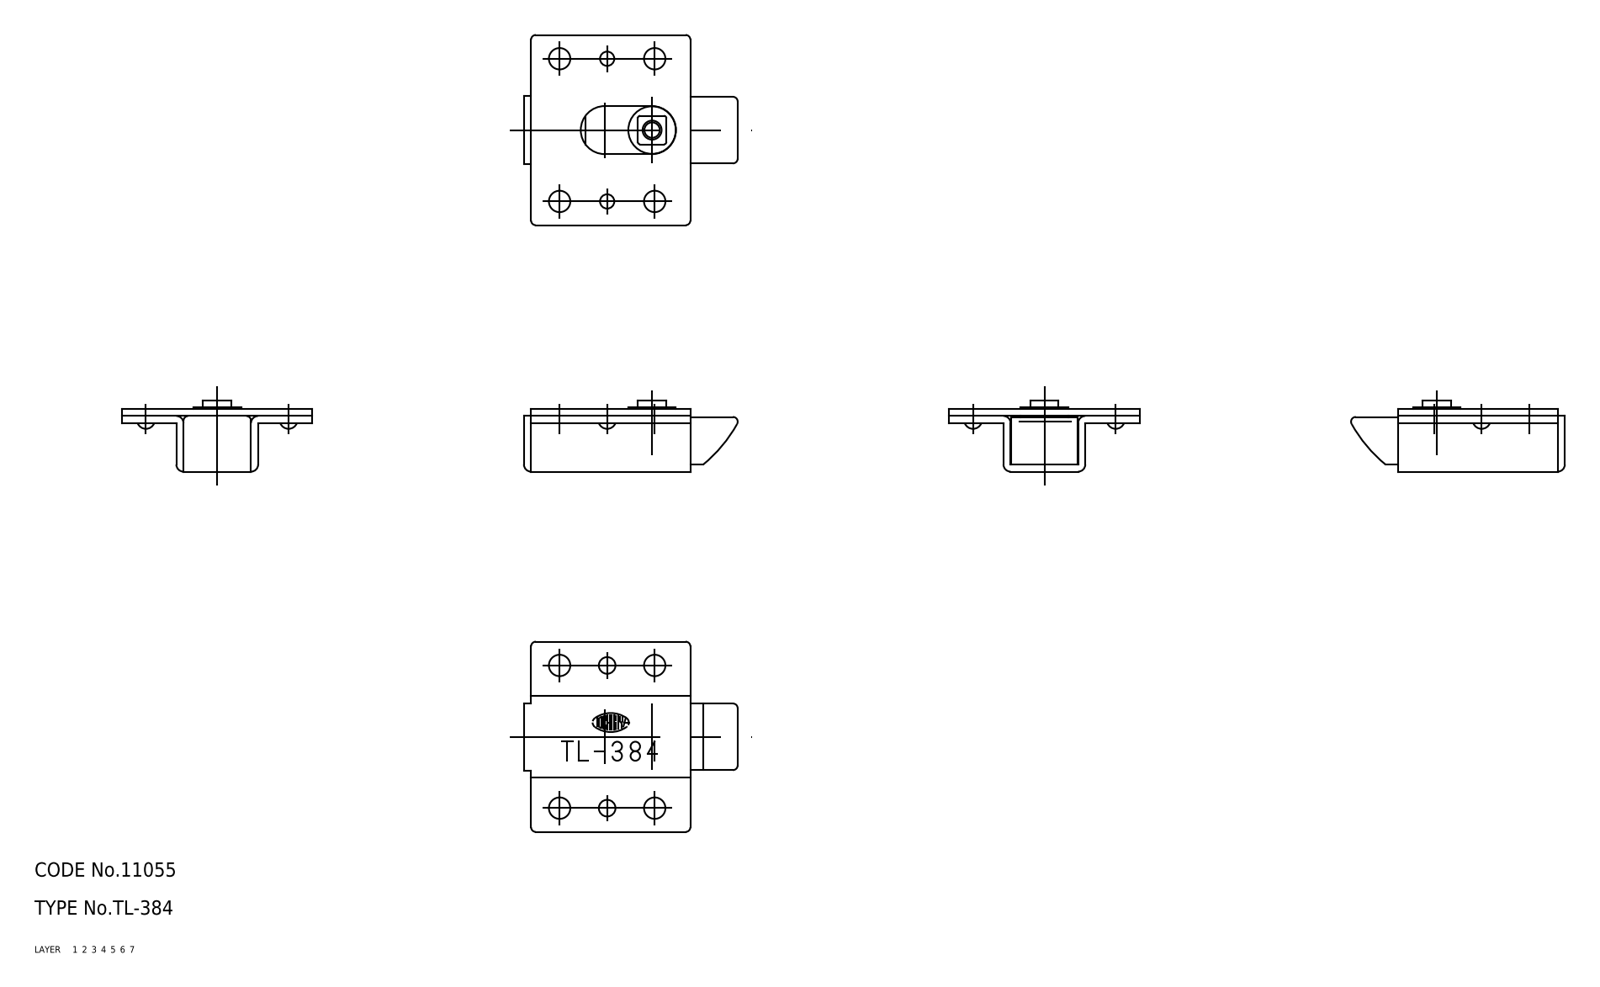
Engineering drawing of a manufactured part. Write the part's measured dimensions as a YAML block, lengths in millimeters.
part_name: "67115101; 67115114; 67115127"
step_written_by: "CADfix (AUTOMOTIVE_DESIGN)"
units: millimeters
bodies: {solids: 3, faces: 111, planar: 0, cylindrical: 0, other: 111}
overall_size: [44.95, 40, 14.9]
volume: 8929
surface_area: 8959
